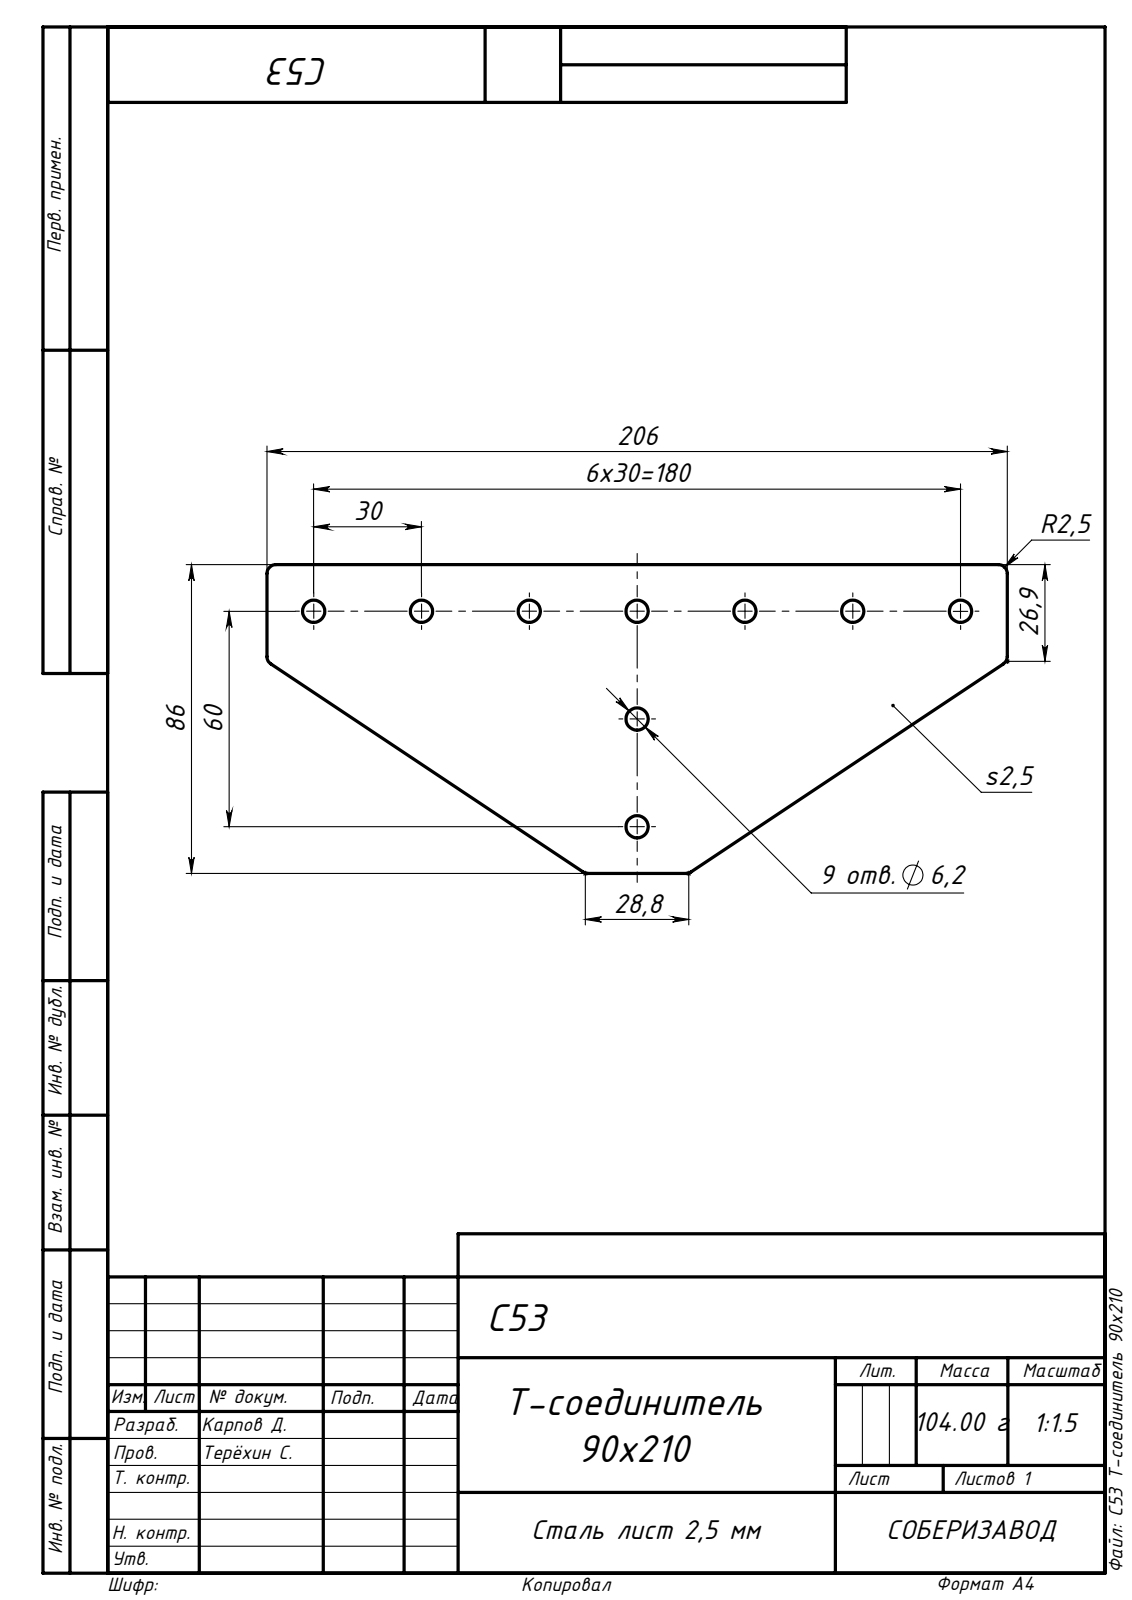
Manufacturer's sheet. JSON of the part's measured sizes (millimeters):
{"part_name": "C53 Т-соединитель 90х210", "step_written_by": "SolidWorks 2019 (AUTOMOTIVE_DESIGN)", "units": "millimeters", "bodies": {"solids": 1, "faces": 32, "planar": 8, "cylindrical": 24, "other": 0}, "overall_size": [206, 86, 2.5], "volume_mm3": 30517, "surface_area_mm2": 26100, "round_holes": [[6.2, 9]], "partial_cylinders_radius": [[2.5, 6]], "face_to_face_distances": [2.5, 86, 206], "hole_center_spacings": [30, 60, 67.08, 90, 120, 42.43, 84.85, 94.87]}
